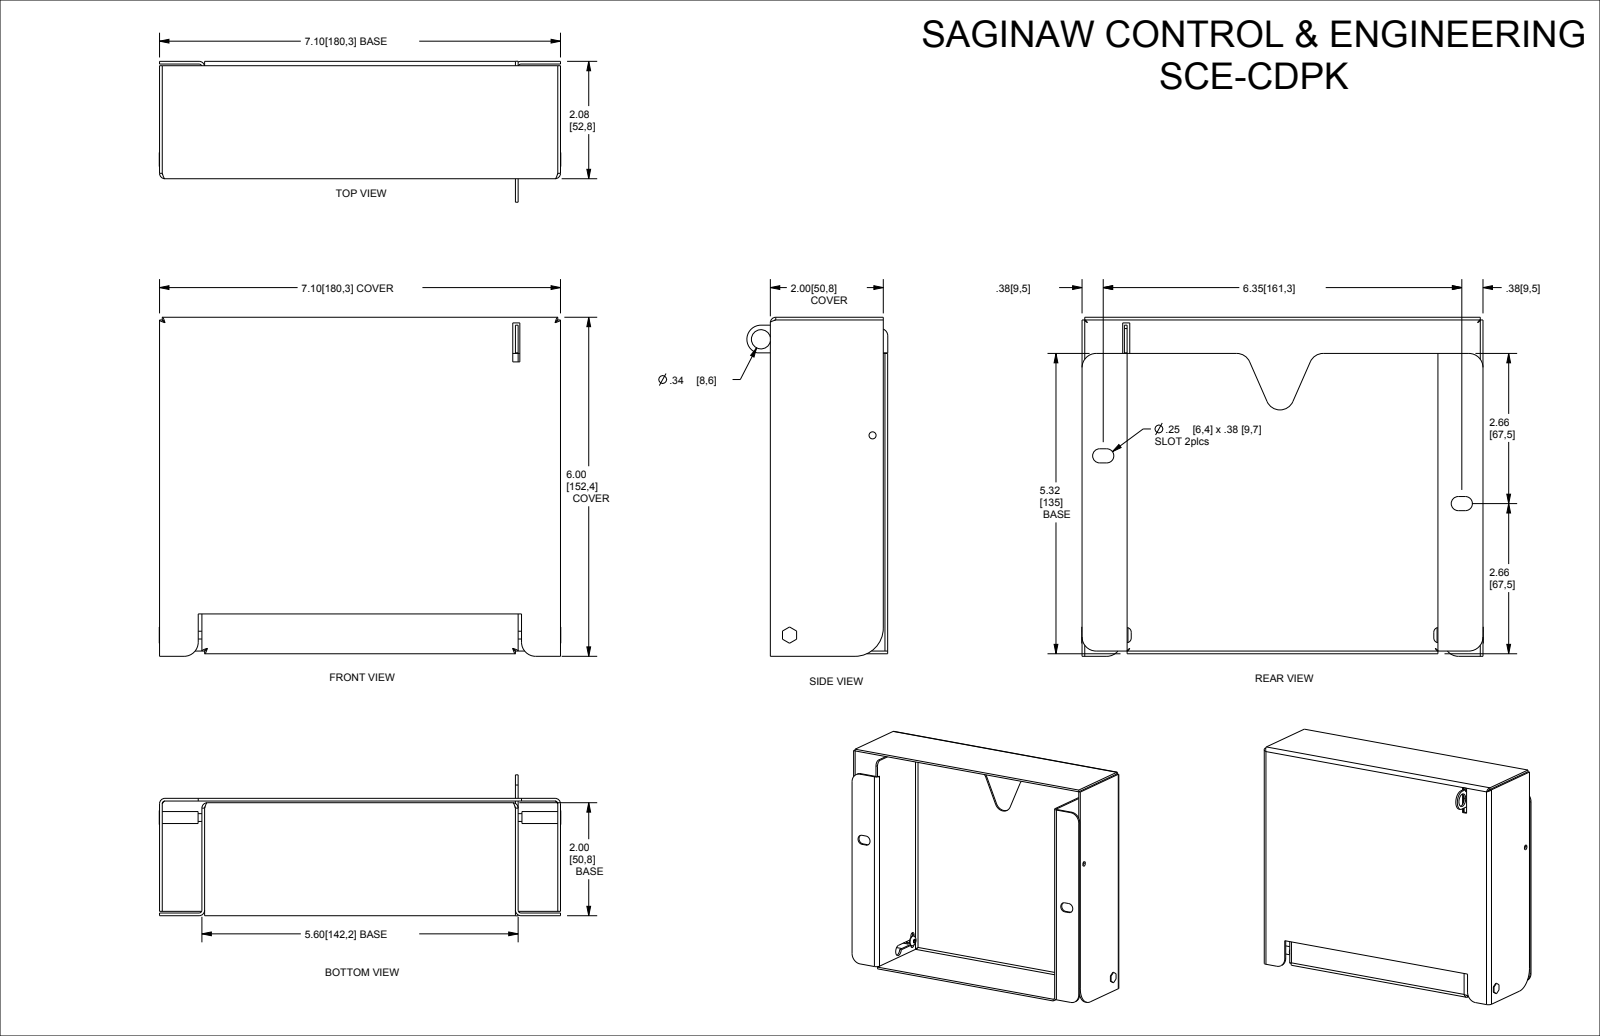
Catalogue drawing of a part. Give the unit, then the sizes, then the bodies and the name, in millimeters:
Units: millimetres
Overall size (bounding box): 180.6 × 152.4 × 63.4
Round holes (diameter × count): ⌀3.2 ×1, ⌀3.5 ×1, ⌀5.4 ×1, ⌀8.6 ×1
Round bosses / shafts (diameter × count): ⌀6.7 ×1, ⌀5.4 ×1
Partial cylindrical surfaces — rounded edges, fillets, slot ends (radius × count): R6.4 ×10, R2.4 ×6, R3.2 ×4, R1.2 ×3, R1.3 ×2, R2 ×2, R2.5 ×2, R3.3 ×1
Main face-to-face distances: 1.2, 2, 19.1, 160.1, 0.8, 3.2, 179.1, 150, 20.3, 158.9
Hole centre spacings: 66.2, 97.2, 133.6
Bodies: 0 solids, 198 faces (106 planar, 61 cylindrical, 31 other)
Part name (STEP PRODUCT): SCE-CDPK
STEP written by: SolidWorks 2019 (AUTOMOTIVE_DESIGN)
